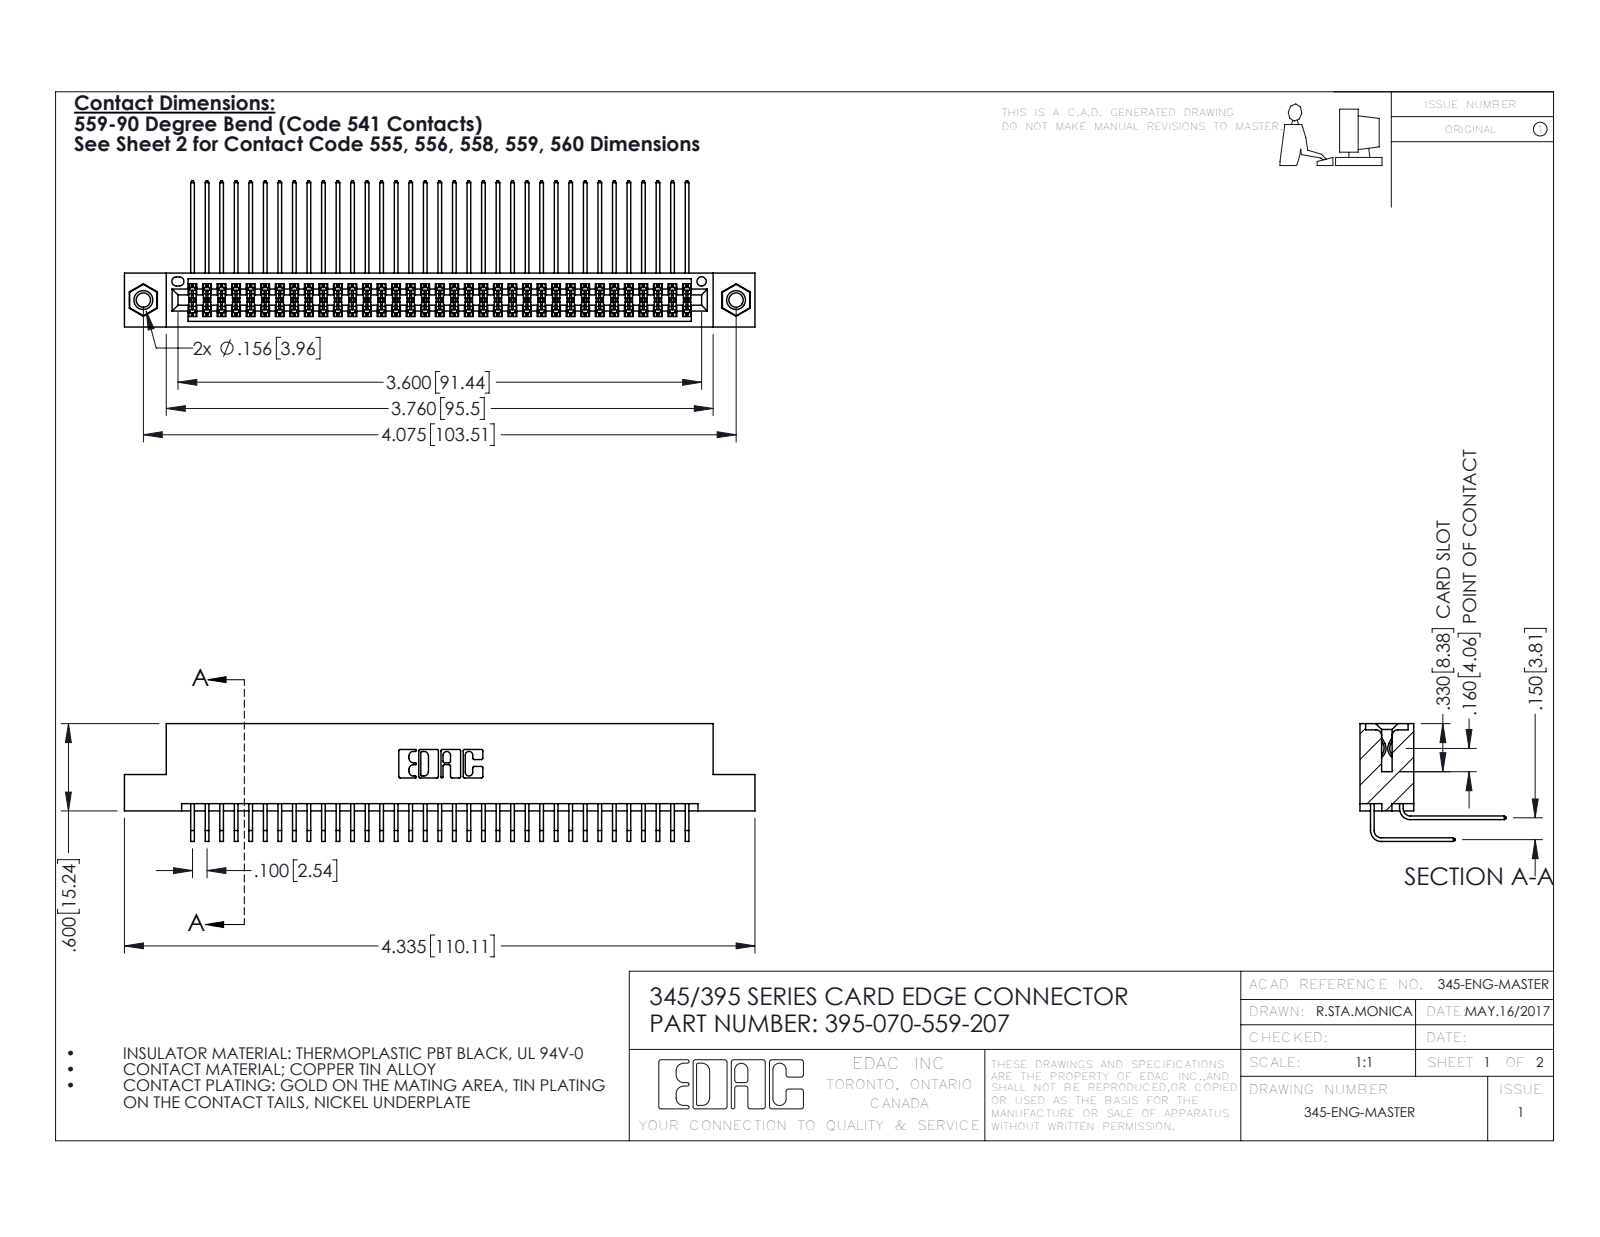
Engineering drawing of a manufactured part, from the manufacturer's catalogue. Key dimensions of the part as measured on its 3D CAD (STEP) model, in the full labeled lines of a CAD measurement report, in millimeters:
Part name (STEP PRODUCT): 345-250-001_345-250-005-103; 345 Part_Flush Mounting Lugs - 0.156 Dia-TI; 395-070-559-207; 345-292-001_559 Tail - 2 (+1 more)
STEP written by: SolidWorks 2016 (CONFIG_CONTROL_DESIGN)
Units: millimetres
Bodies: 73 solids, 3826 faces (2562 planar, 1248 cylindrical, 16 other)
Overall size (bounding box): 110.1 × 25.5 × 20.5
Volume: 11 000 mm³ · Surface area: 18 080 mm²
Round holes (diameter × count): ⌀2.5 ×2, ⌀3.2 ×2, ⌀4 ×2, ⌀1.6 ×1
Round bosses / shafts (diameter × count): ⌀3.9 ×2
Partial cylindrical surfaces — rounded edges, fillets, slot ends (radius × count): R0.2 ×105, R0.3 ×22, R0.2 ×6, R0.8 ×6, R0.7 ×3, R0.4 ×2, R0.5 ×2, R0.6 ×2
Main face-to-face distances: 1.8, 7.6, 5.1, 9.4, 2.5, 6.9, 0.6, 5.7, 4.4, 3.8
Hole centre spacings: 6.9, 97.5, 103.5
